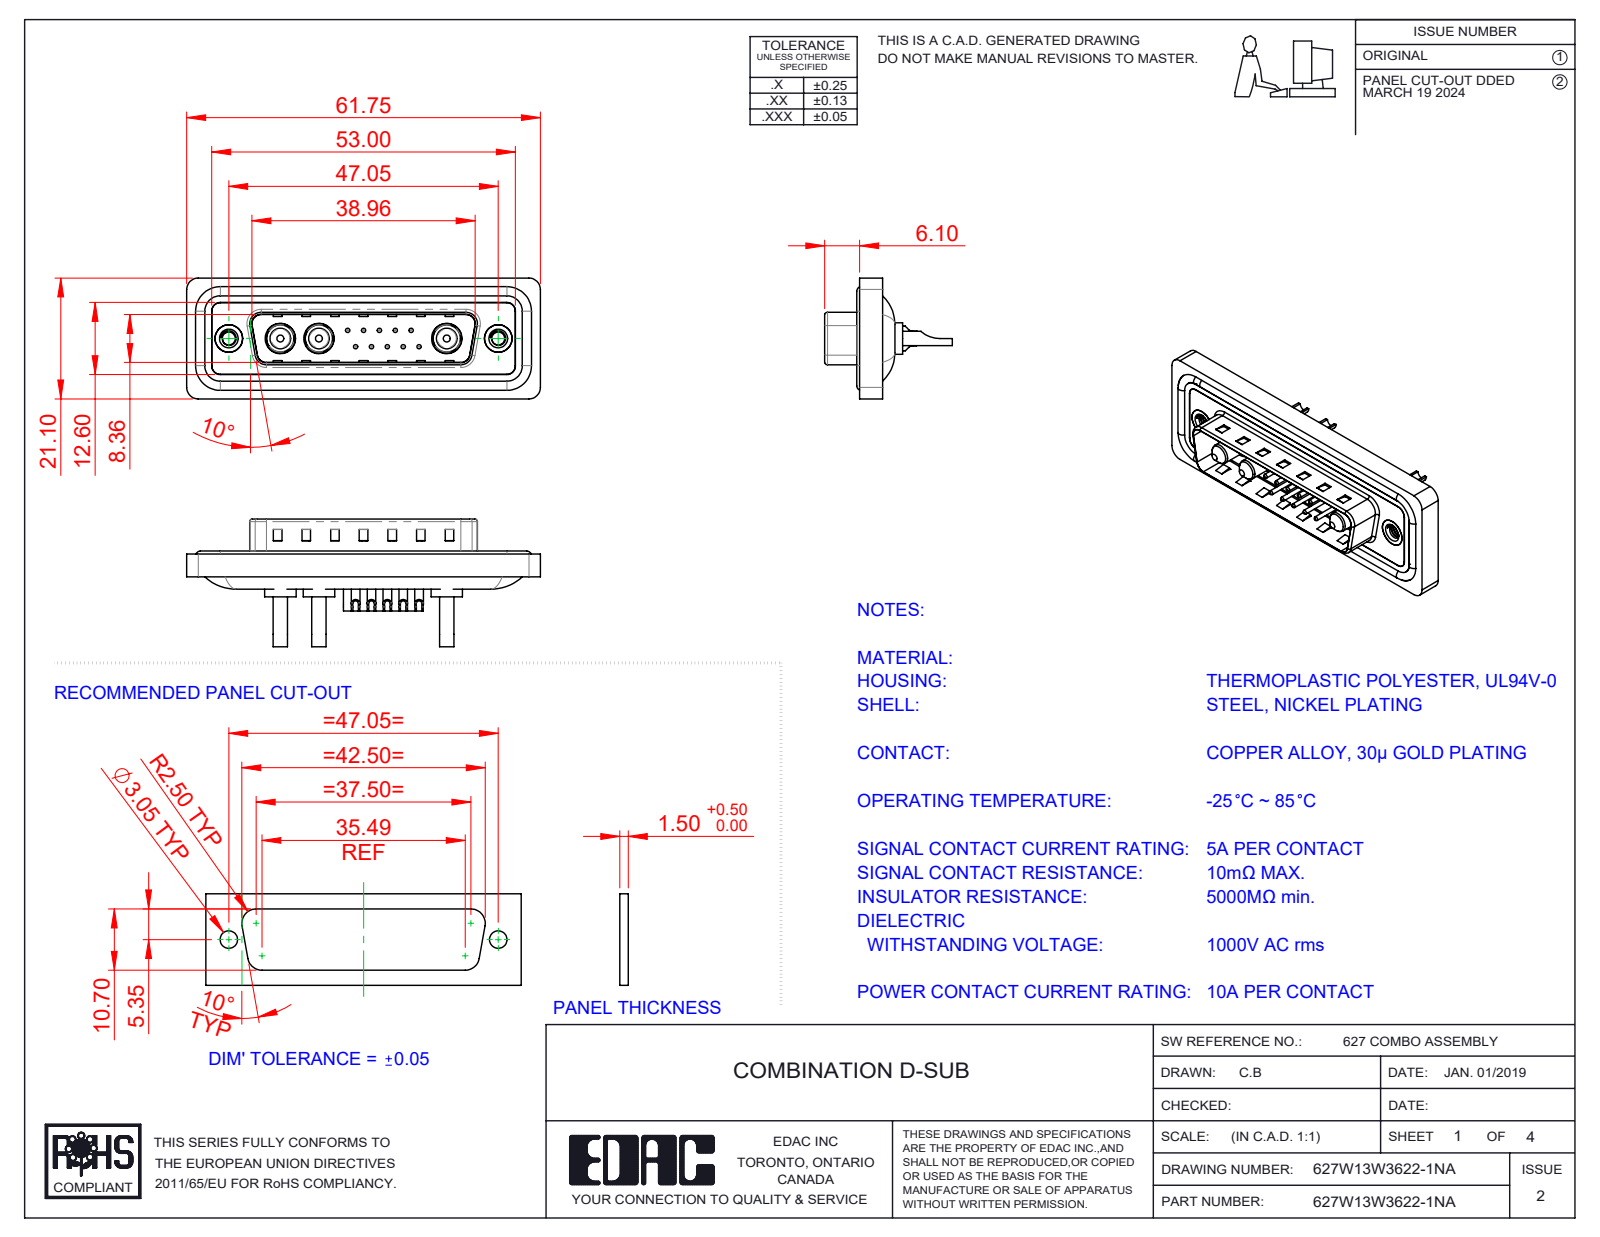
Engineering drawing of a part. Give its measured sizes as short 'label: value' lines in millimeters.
name: 627Combo Threaded Rivet_A; 627Combo Housing_13W3; 627W13W3622-1NA; 627Combo Contact Row 1_22 (+5 more)
written by: SolidWorks 2023 (CONFIG_CONTROL_DESIGN)
unit: mm
bodies: 23 solids, 986 faces (335 planar, 416 cylindrical, 235 other)
size: 61.75 × 22.3 × 21.1
volume: 7 344 mm³; area: 12 095 mm²
holes: 10× ⌀0.75, 10× ⌀1, 10× ⌀1.6, 10× ⌀2, 3× ⌀1.7, 3× ⌀4.85, 3× ⌀5.3, 2× ⌀2.26, 2× ⌀4, 2× ⌀4.8, 2× ⌀5
bosses: 10× ⌀1.5, 4× ⌀1.6, 3× ⌀5.5, 3× ⌀5.2, 3× ⌀4.75, 3× ⌀3.75, 3× ⌀3.6, 3× ⌀2.5
rounds: 22× R1.5, 18× R2, 8× R0.5, 8× R1.6, 6× R1, 4× R0.25, 4× R0.6, 4× R0.65
face distances: 0.4, 1.5, 1.1, 1.6, 0.5, 3.1, 2.9, 0.82, 9.58, 4.1
hole spacings: 3.16, 2.77, 5.04, 5.54, 7.49, 5.03, 8.31, 10.11
